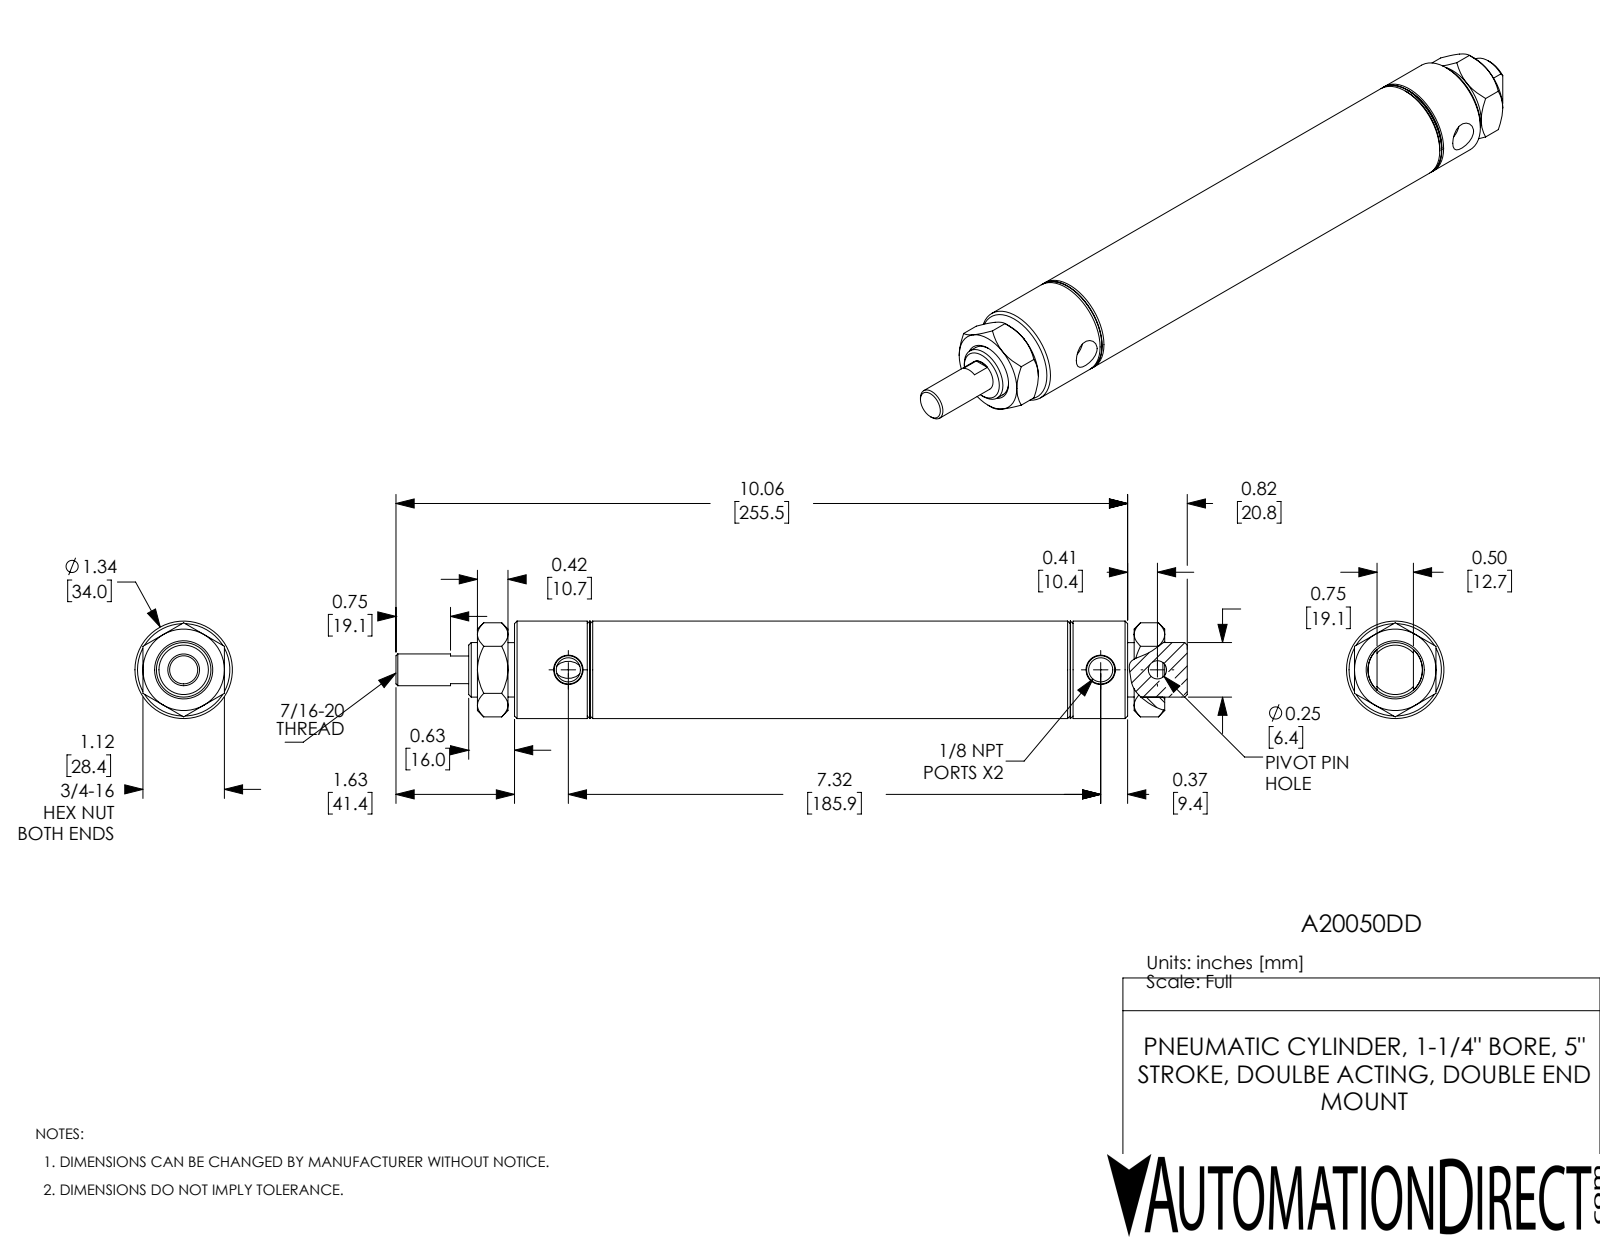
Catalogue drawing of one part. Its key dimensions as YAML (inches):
part_name: "A20050DD_Mounting Nut_D-3556; A20050DD; A20050DD-MainBody; A20050DD-Rod"
step_written_by: "SolidWorks 2017 (AUTOMOTIVE_DESIGN)"
units: inches
bodies: {solids: 4, faces: 138, planar: 44, cylindrical: 36, other: 58}
overall_size: [10.88, 1.34, 1.34]
volume: 7.604
surface_area: 92.9
round_holes:
  - {diameter: 0.332, count: 2}
  - {diameter: 0.251, count: 1}
  - {diameter: 0.437, count: 1}
  - {diameter: 0.75, count: 1}
  - {diameter: 1.25, count: 1}
round_bosses_or_shafts:
  - {diameter: 1.34, count: 1}
  - {diameter: 0.747, count: 1}
face_to_face_distances: [1.465, 6.965, 0.5, 1.12, 5.5, 5, 0.31, 0.42, 9.03, 1.965]
hole_center_spacings: [0.78, 7.32, 8.1]
